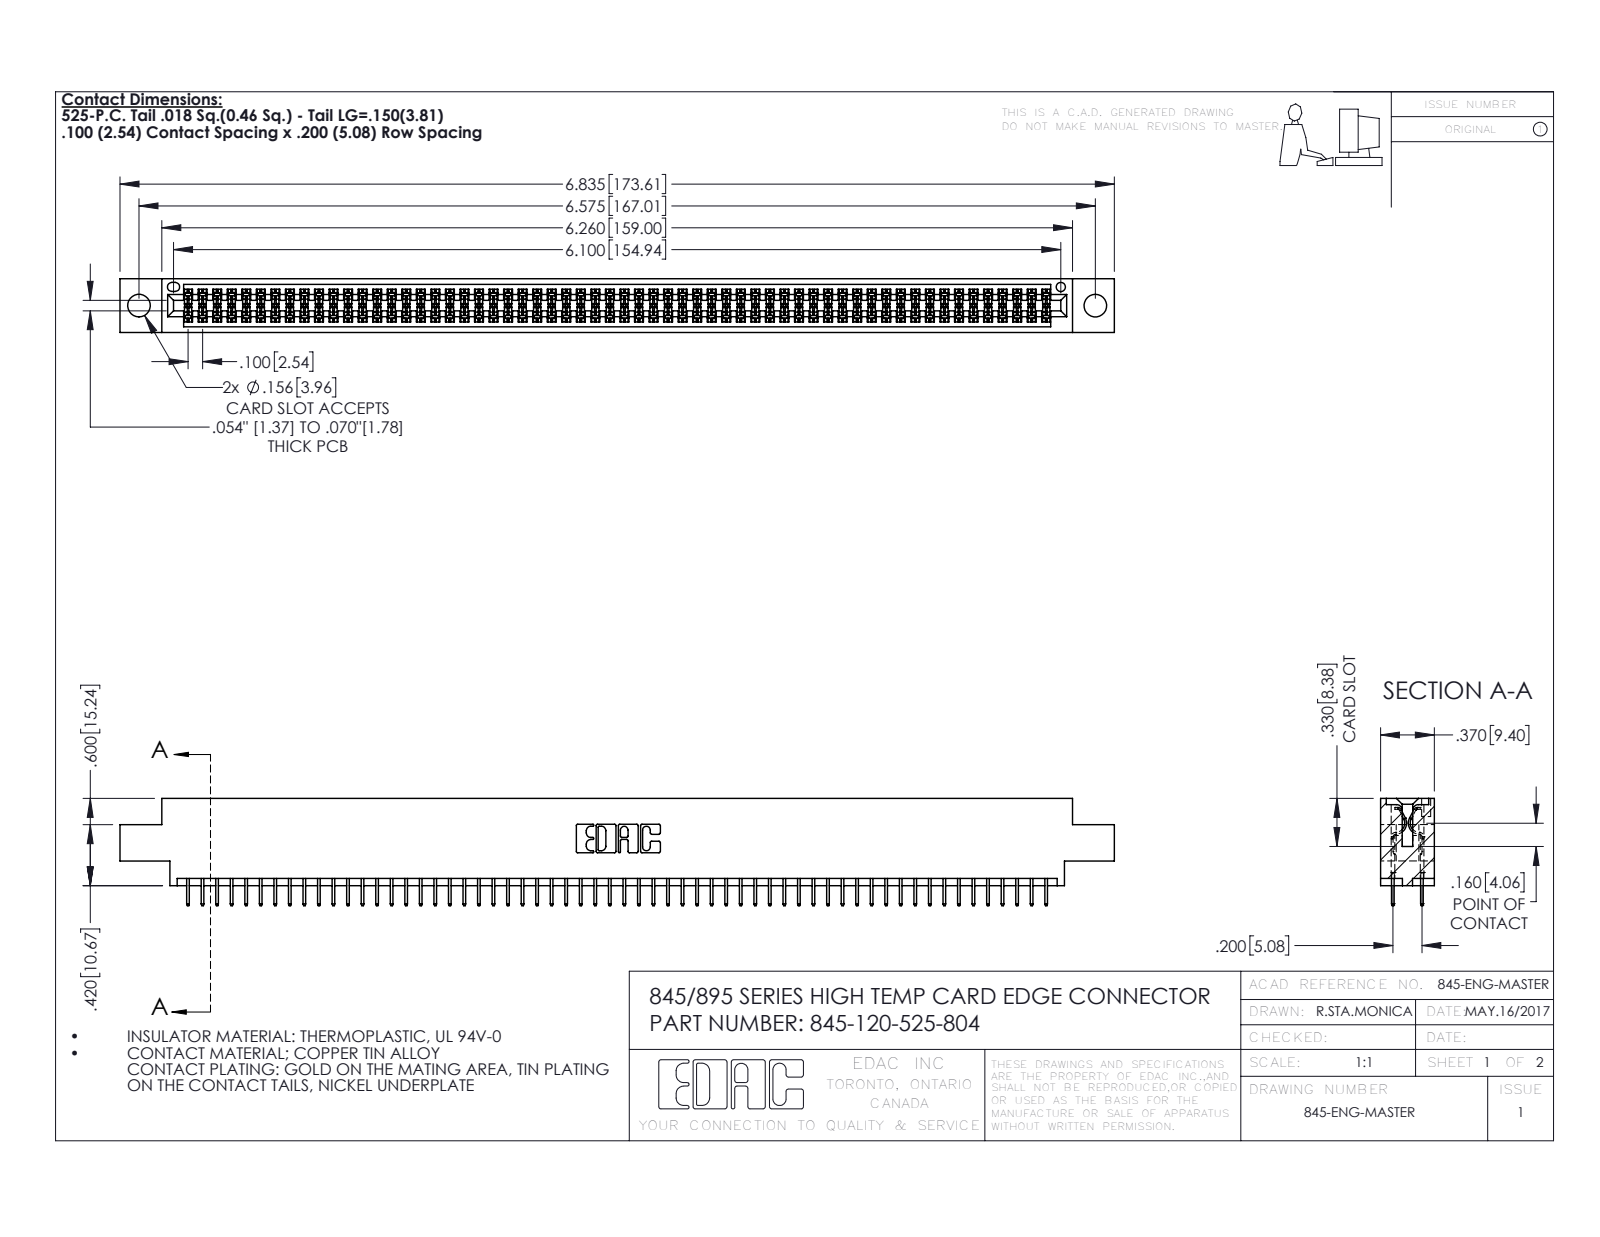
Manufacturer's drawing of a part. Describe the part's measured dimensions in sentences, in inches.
The part is named "345-292-001_345-293-125; 845-120-525-804; 845 Part_0.170 Offset - 0.156 Dia-TH". Its 3-D file was written by "SolidWorks 2020 (CONFIG_CONTROL_DESIGN)". It is 121 solids with 6610 faces: 4764 planar, 1846 cylindrical and 0 other. Overall it measures 6.835 by 0.737 by 0.37 inches. Its volume is 1.015 cubic inches and its surface area 37.66 square inches. Round holes: 2 of diameter 0.156, 1 of diameter 0.064. Partial cylindrical surfaces (rounded edges, fillets, slot ends): 180 of radius 0.006, 22 of radius 0.01, 6 of radius 0.007, 6 of radius 0.031, 3 of radius 0.026, 2 of radius 0.014, 2 of radius 0.019, 2 of radius 0.022. The main face-to-face distances are 0.072, 0.298, 0.37, 0.2, 0.098, 0.272, 0.025, 0.225, 0.175, 0.072. The hole center spacings are 0.27, 6.339, 6.575.
